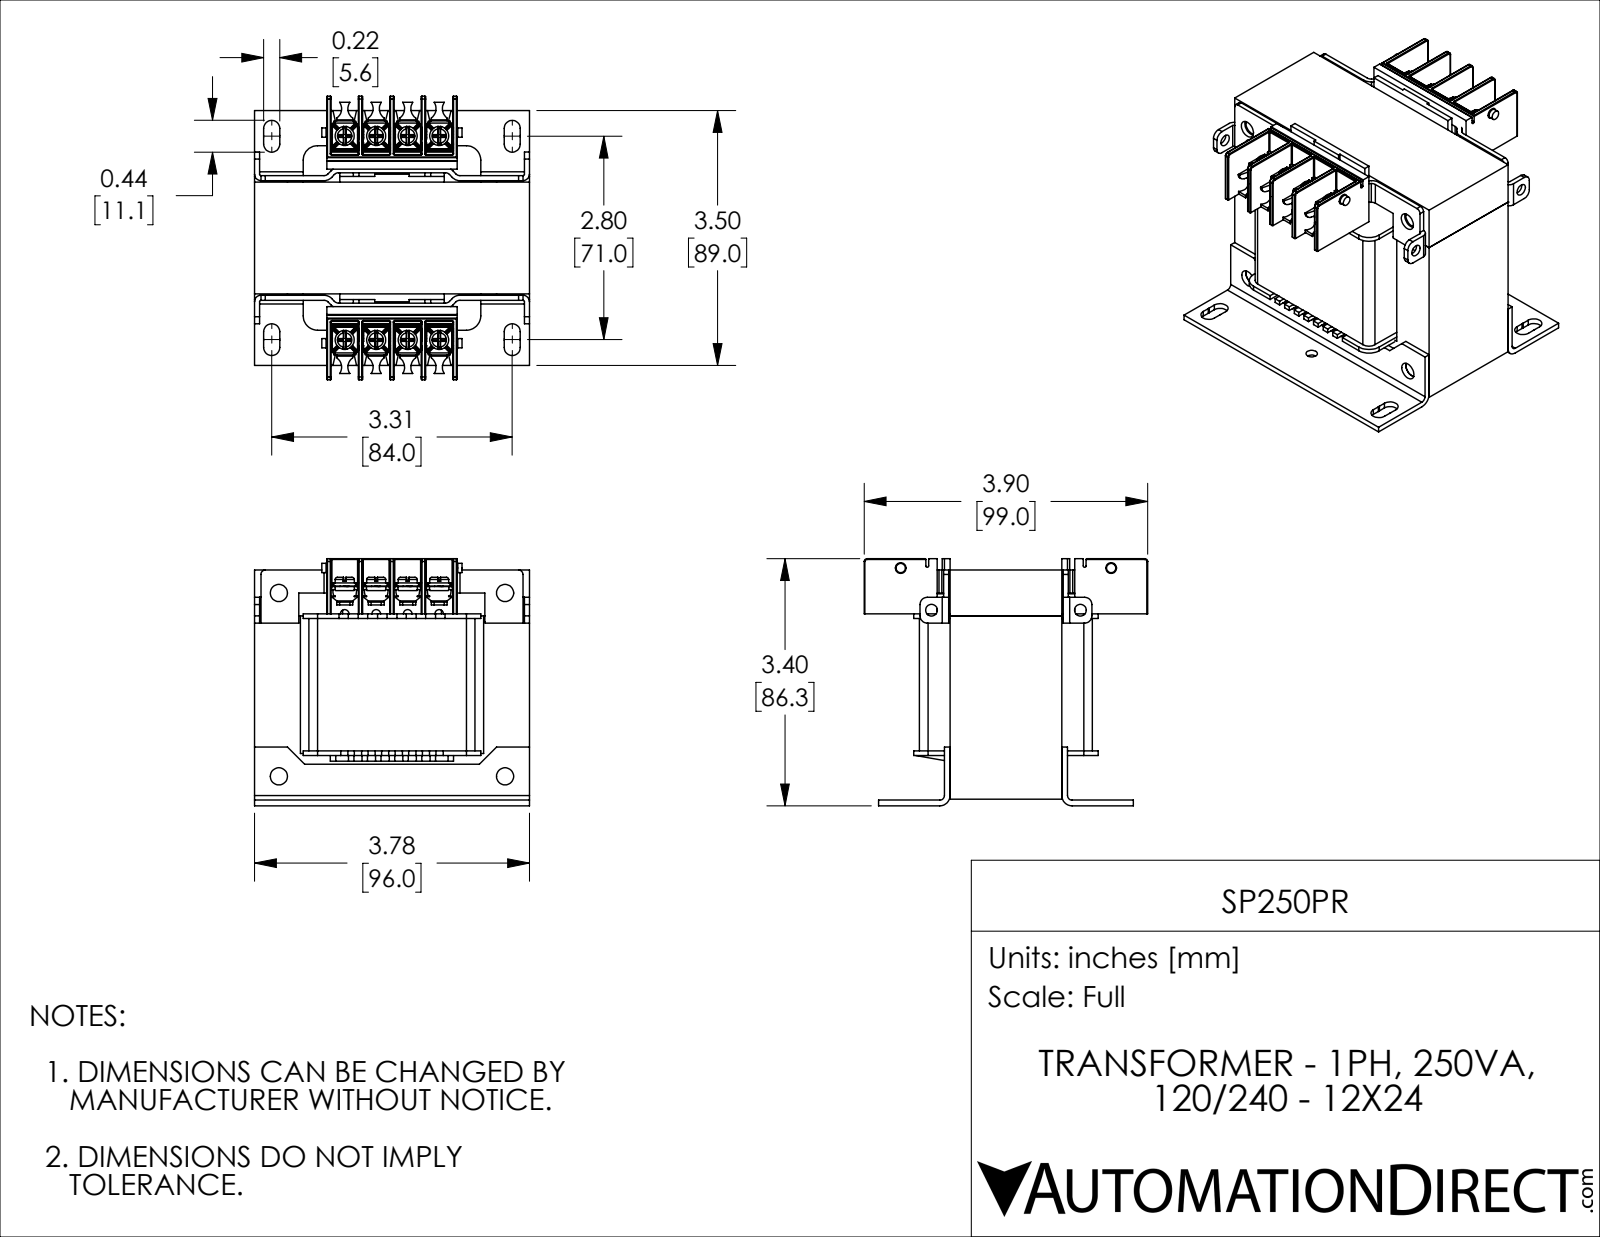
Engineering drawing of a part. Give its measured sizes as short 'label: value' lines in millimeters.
name: SP250PR
written by: SolidWorks 2018 (AUTOMOTIVE_DESIGN)
unit: mm
bodies: 41 solids, 3222 faces (1990 planar, 934 cylindrical, 298 other)
size: 99 × 96 × 86.3
volume: 395 600 mm³; area: 117 900 mm²
holes: 10× ⌀4, 8× ⌀2.7, 8× ⌀3.5, 4× ⌀6, 2× ⌀4.1
bosses: 8× ⌀6.7, 8× ⌀6.1, 8× ⌀4.3, 8× ⌀2.8, 2× ⌀3.3
rounds: 62× R0.3, 52× R0.1, 42× R0.3, 32× R0.7, 16× R4, 12× R0.9, 12× R1.7, 10× R2
face distances: 16, 64, 39, 80, 2, 32, 48, 1.5, 19, 77
hole spacings: 11, 22, 71.8, 33, 70.9, 74.3, 71.6, 72
